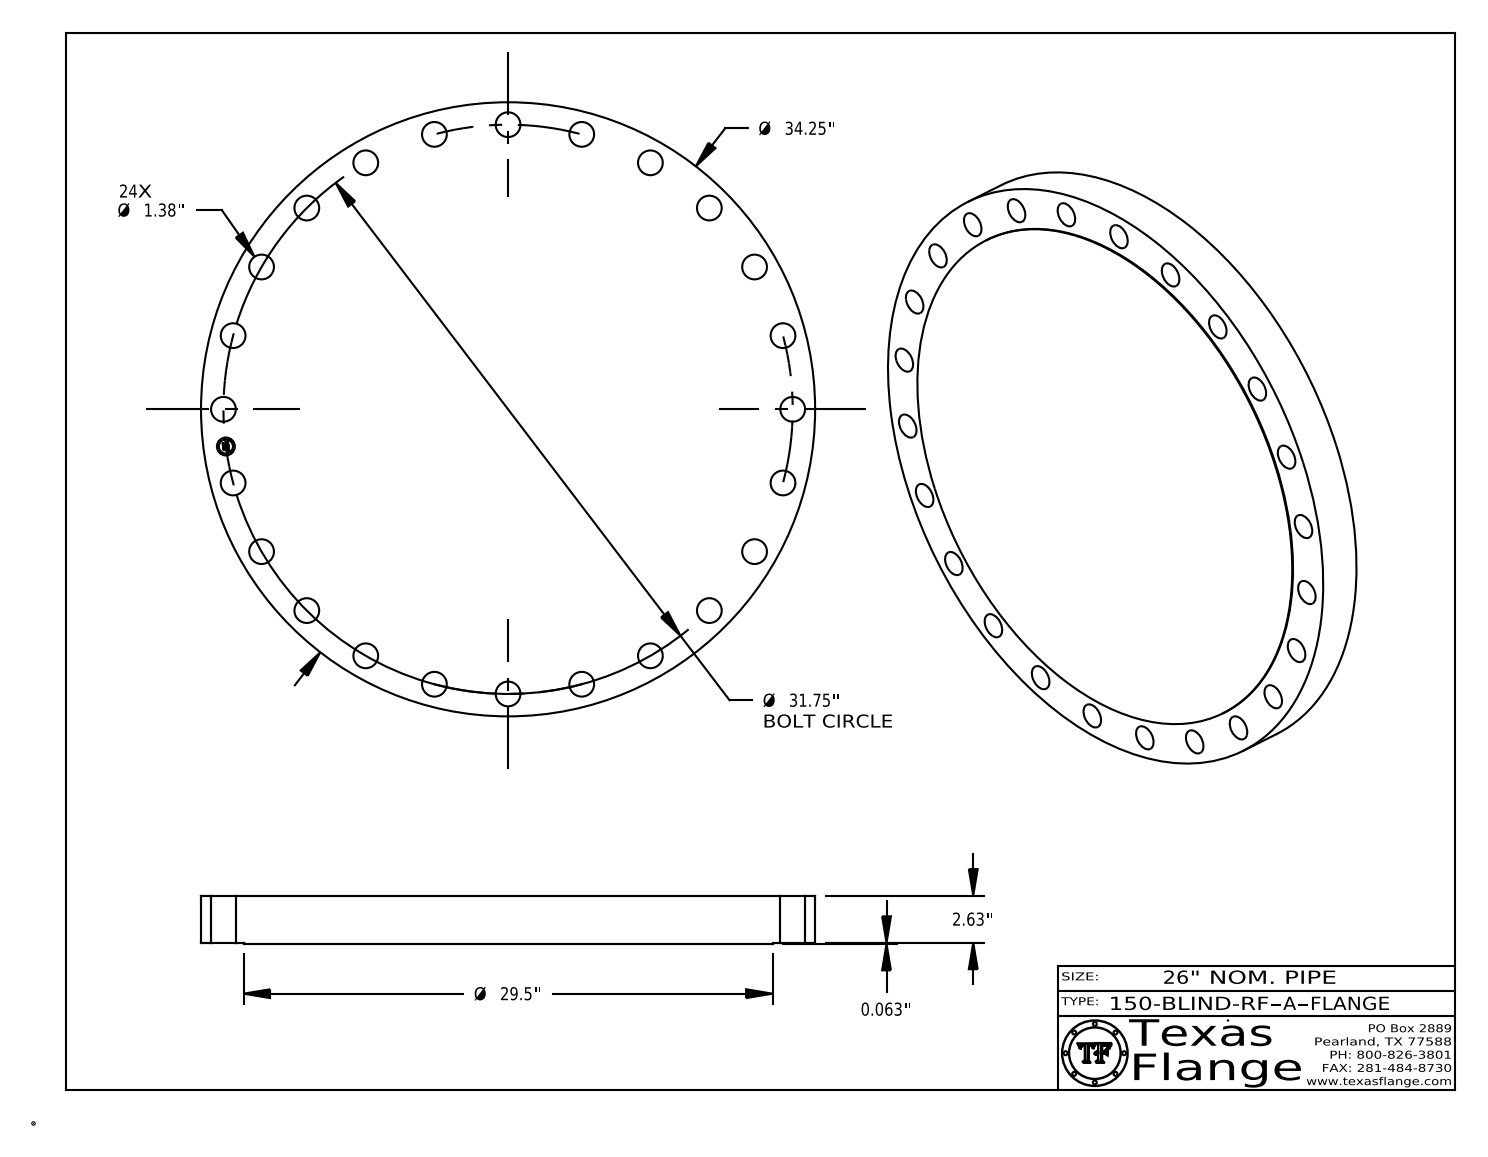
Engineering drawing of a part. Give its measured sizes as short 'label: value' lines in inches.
name: 150-BLIND-RF, Series A
written by: CATIA V5 STEP AP214 (AUTOMOTIVE_DESIGN)
unit: in
bodies: 1 solid, 440 faces (368 planar, 72 cylindrical, 0 other)
size: 34.25 × 34.25 × 2.693
volume: 2 372 in³; area: 2 334 in²
holes: 24× ⌀1.38, 1× ⌀1
bosses: 8× ⌀0.061, 1× ⌀34.25, 1× ⌀29.5, 1× ⌀0.788
face distances: 2.693, 0.063, 2.63, 2.678, 2.615, 0.015, 0.298, 0.292, 0.054, 0.193
hole spacings: 29.333, 27.496, 4.144, 8.217, 12.15, 19.328, 25.189, 30.668
